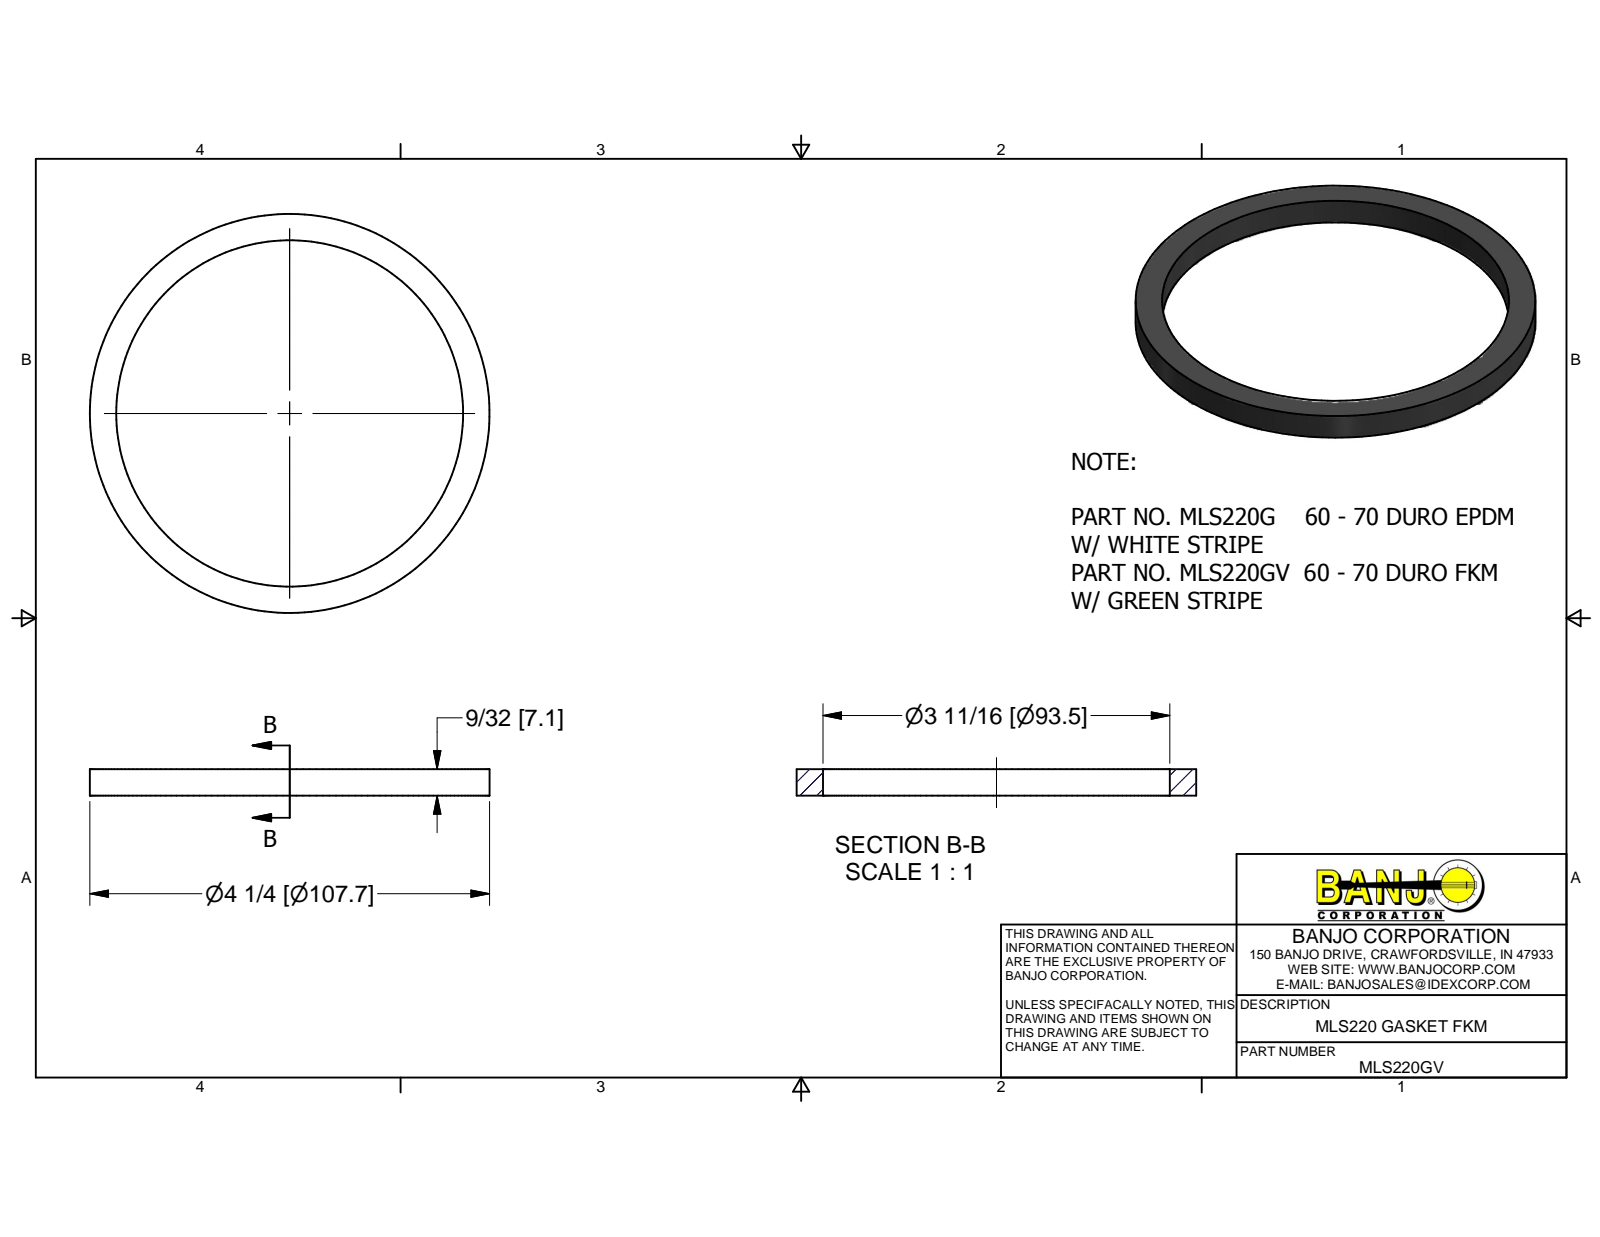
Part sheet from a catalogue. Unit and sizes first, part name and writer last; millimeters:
Units: millimetres
Overall size (bounding box): 107.7 × 107.7 × 7.14
Round holes (diameter × count): ⌀93.47 ×1
Round bosses / shafts (diameter × count): ⌀107.7 ×1
Main face-to-face distances: 7.14
Volume: 16 040 mm³ · Surface area: 9 005 mm²
Bodies: 1 solid, 4 faces (2 planar, 2 cylindrical, 0 other)
Part name (STEP PRODUCT): MLS220GV
STEP written by: Autodesk Inventor 2016 (AUTOMOTIVE_DESIGN)
